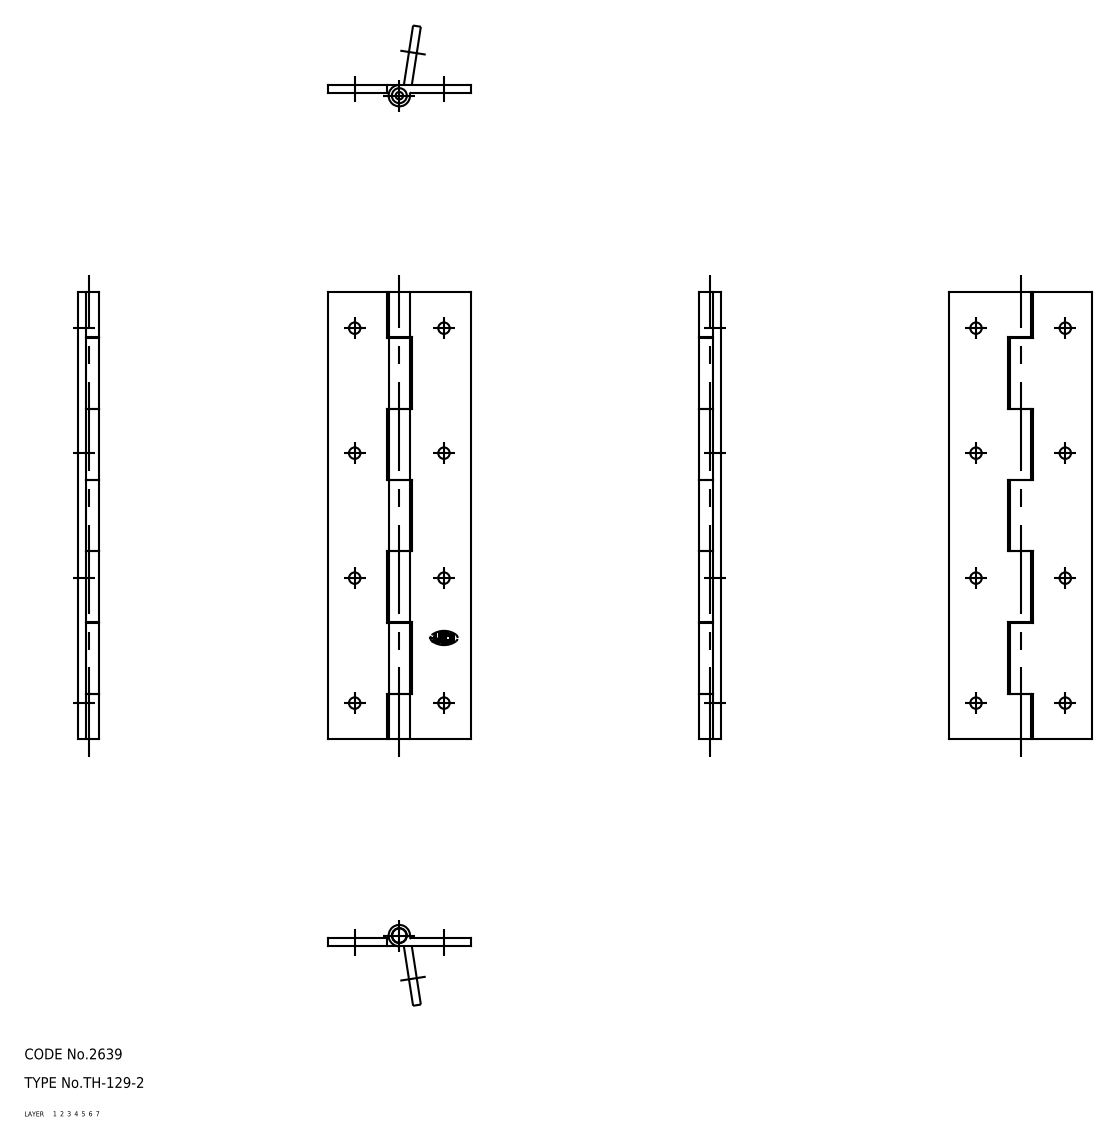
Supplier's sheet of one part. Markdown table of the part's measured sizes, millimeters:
| quantity | value |
| --- | --- |
| part name | shaft; hinge piece_B; hinge piece_A; TH_129_2_3141_36 |
| STEP written by | CADfix (AUTOMOTIVE_DESIGN) |
| units | millimeters |
| bodies | 3 solids, 76 faces (0 planar, 0 cylindrical, 76 other) |
| overall size | 125 × 40 × 6 |
| volume | 12 818 mm³ |
| surface area | 14 353 mm² |
